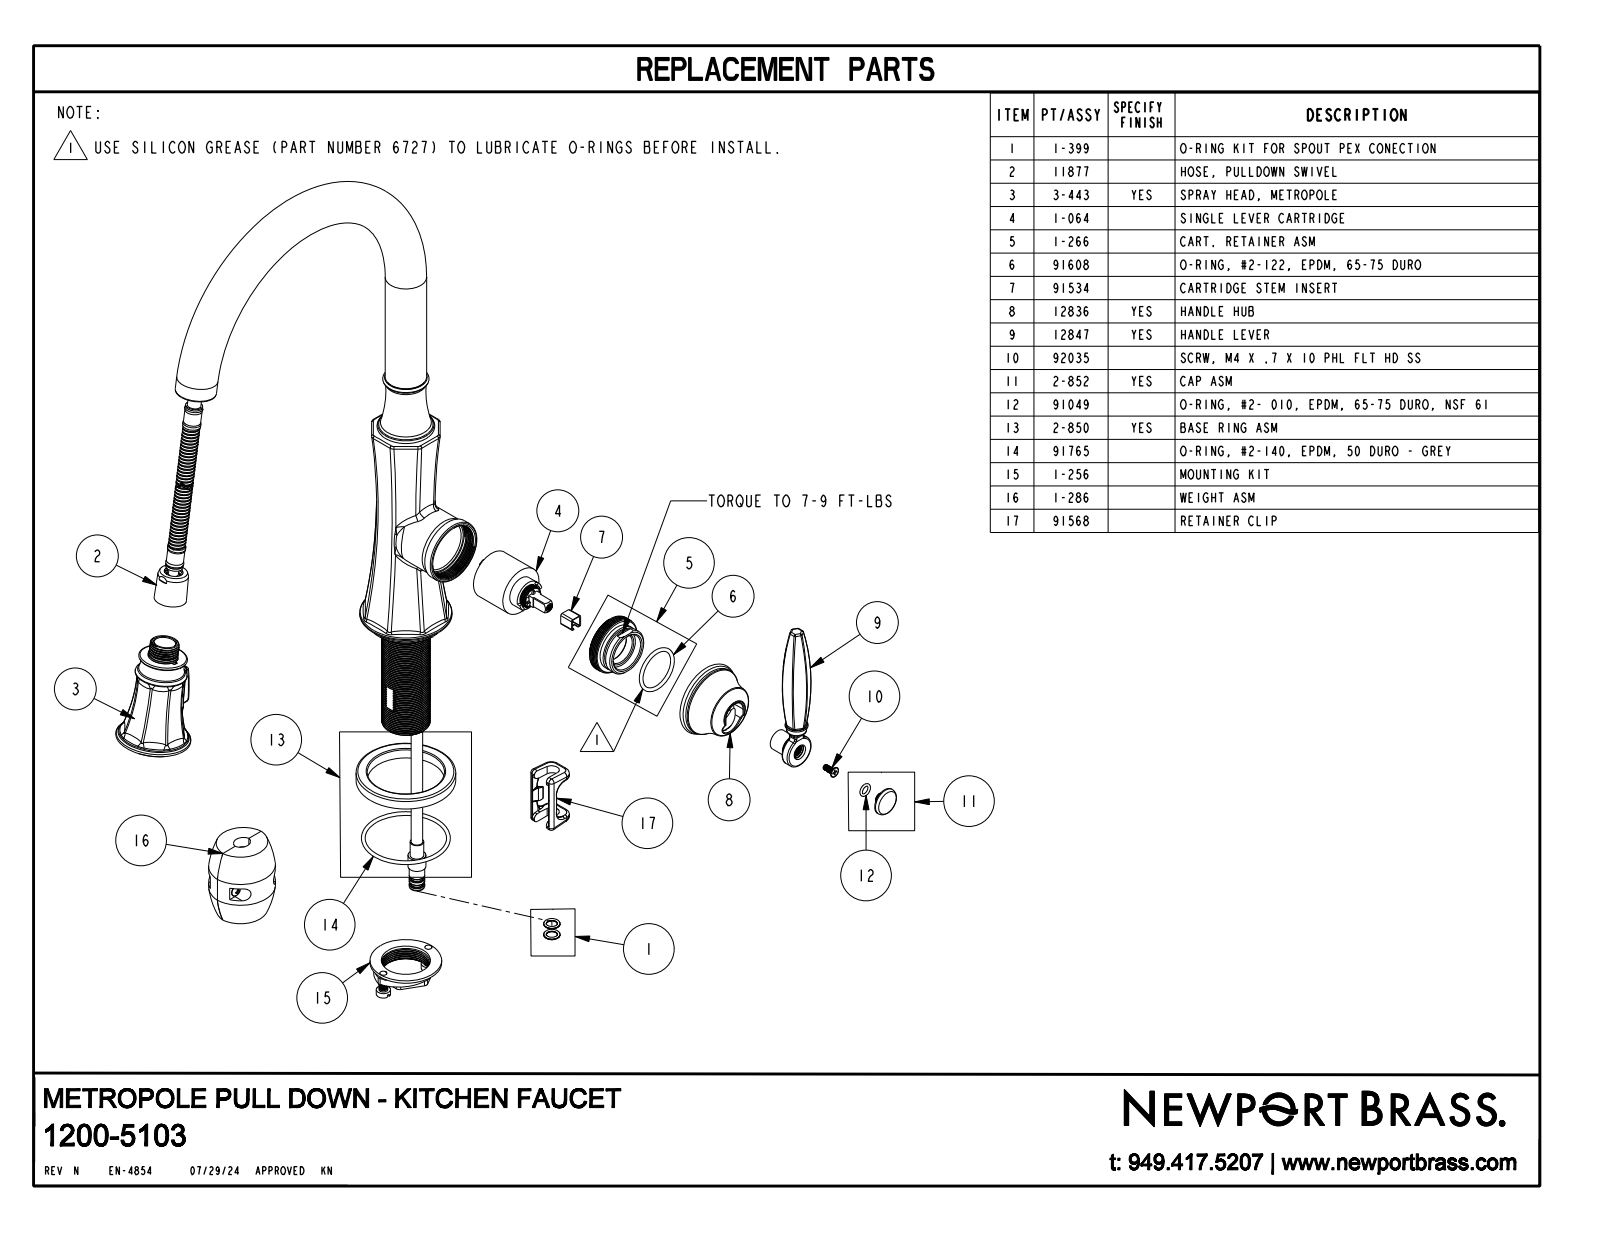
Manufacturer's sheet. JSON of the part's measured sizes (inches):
{"part_name": "12038", "step_written_by": "CREO PARAMETRIC BY PTC INC, 2018400 (CONFIG_CONTROL_DESIGN)", "units": "inches", "bodies": {"solids": 1, "faces": 563, "planar": 72, "cylindrical": 38, "other": 453}, "overall_size": [15.832, 10.902, 4.921], "volume_in3": 46.85, "surface_area_in2": 152.4, "round_holes": [[0.492, 1], [1.24, 1]], "round_bosses_or_shafts": [[2.74, 1], [2.538, 1], [1.96, 1], [1.7, 1], [1.228, 1], [1.124, 1], [1.12, 1], [0.917, 1]], "partial_cylinders_radius": [[0.04, 4], [0.02, 2], [0.05, 2], [0.1, 2], [0.337, 2], [2.8, 1]], "face_to_face_distances": [6.563, 8.263, 1.7, 8.283, 1.72, 0.02, 0.025, 2.718, 2.743, 2.725]}
